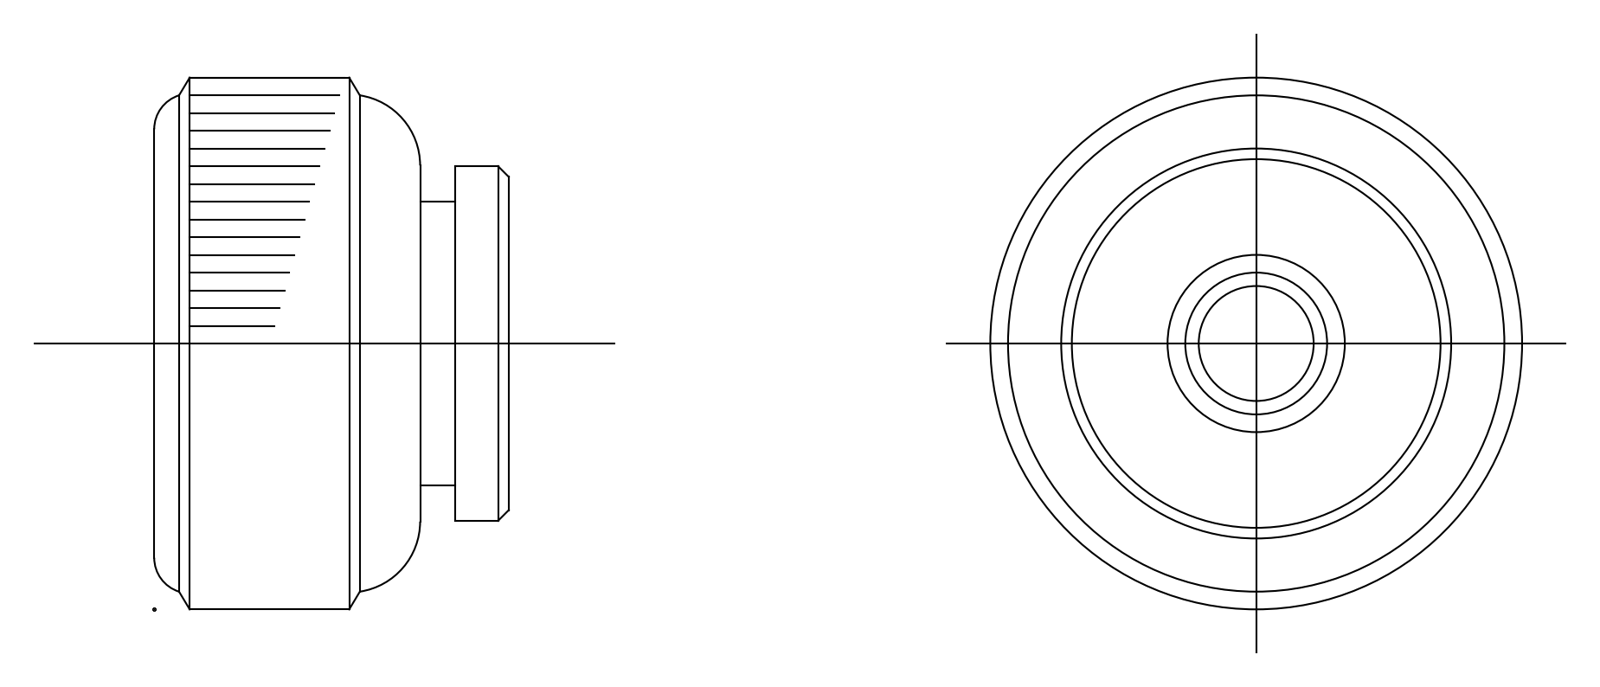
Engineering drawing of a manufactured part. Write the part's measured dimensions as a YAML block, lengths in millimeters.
step_written_by: "spGate 20.6.3 (****-****-****-****) (AUTOMOTIVE_DESIGN)"
units: millimeters
bodies: {solids: 1, faces: 30, planar: 4, cylindrical: 10, other: 16}
overall_size: [15, 15, 10]
volume: 1303
surface_area: 826
round_holes:
  - {diameter: 2.65, count: 1}
  - {diameter: 4, count: 1}
round_bosses_or_shafts:
  - {diameter: 15, count: 1}
  - {diameter: 10, count: 1}
  - {diameter: 8, count: 1}
face_to_face_distances: [10, 7.5, 2.5, 8.5, 1, 1.5]
